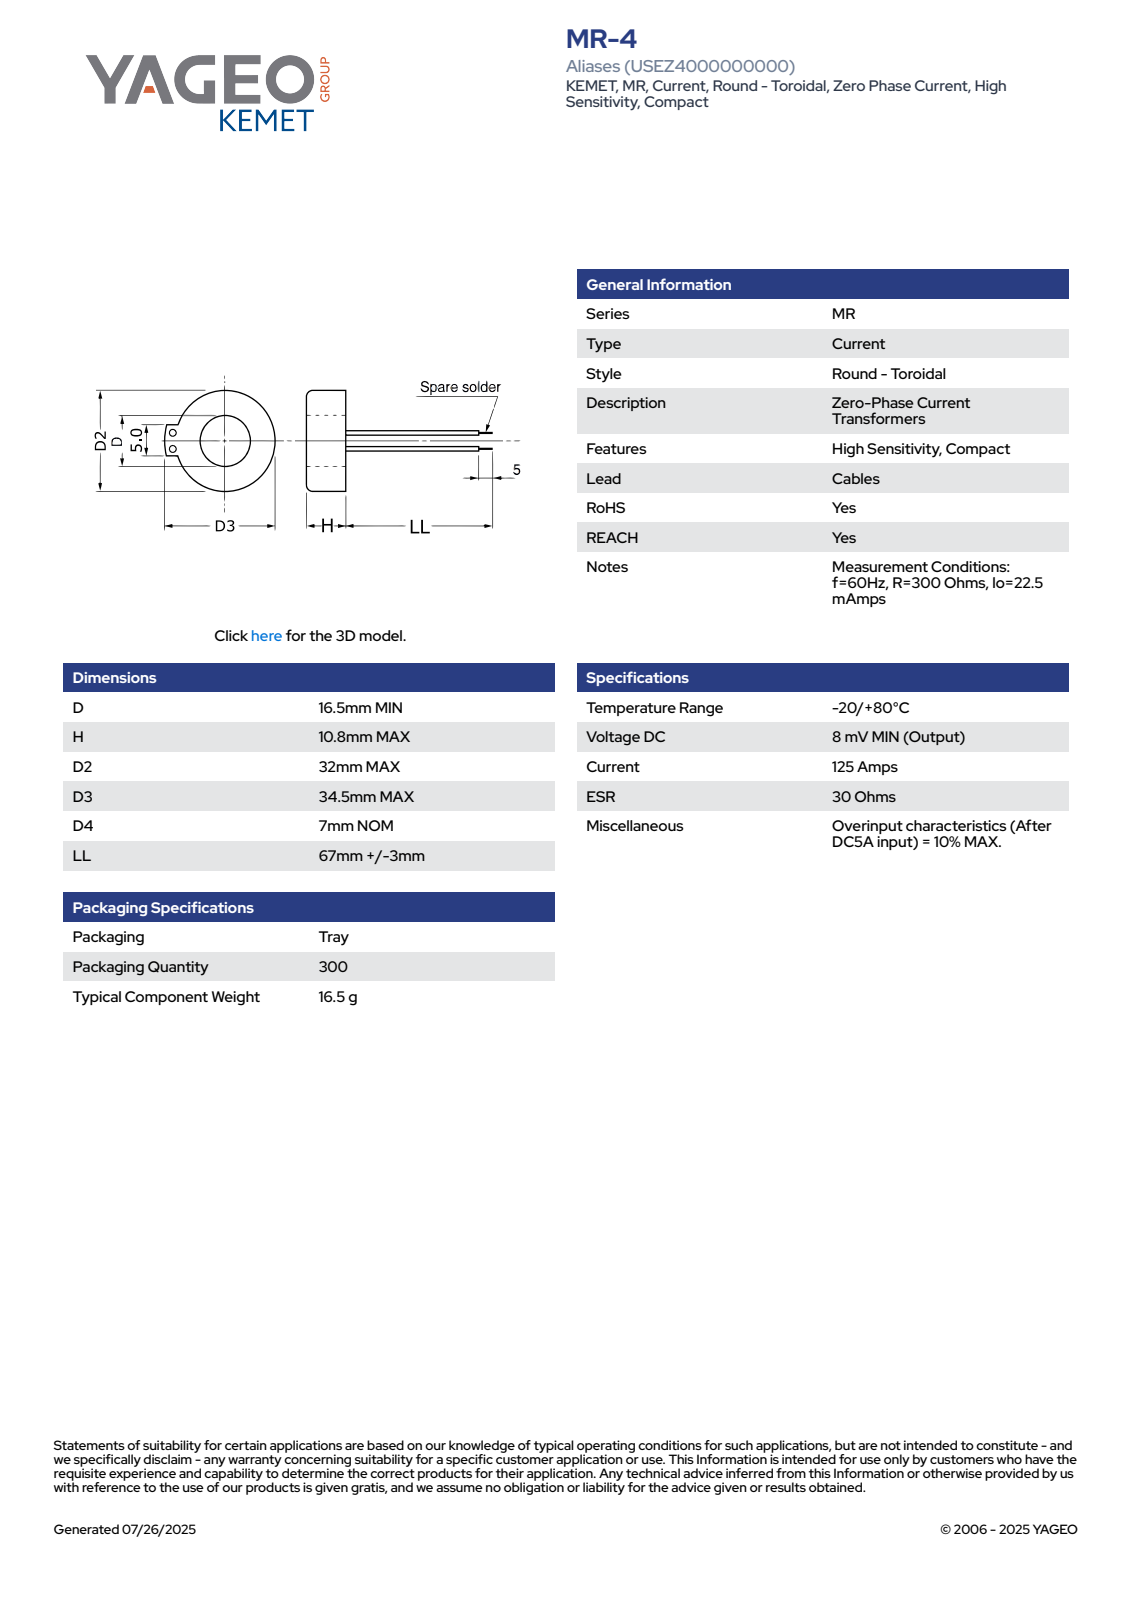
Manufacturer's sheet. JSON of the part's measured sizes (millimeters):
{"part_name": "SC_MR1_D16.5H10.8D232D334.5D47LL70", "step_written_by": "SolidWorks 2014 (AUTOMOTIVE_DESIGN)", "units": "millimeters", "bodies": {"solids": 1, "faces": 84, "planar": 30, "cylindrical": 18, "other": 36}, "overall_size": [80.8, 34.5, 32], "volume_mm3": 6651, "surface_area_mm2": 3302, "round_holes": [[16.5, 1]], "round_bosses_or_shafts": [[1, 2], [0.65, 2], [32, 1]], "partial_cylinders_radius": [[1, 2], [15.99, 1]], "face_to_face_distances": [10.8, 7, 65, 75.8, 5, 70, 80.8, 4.39, 6.41, 76.41]}
